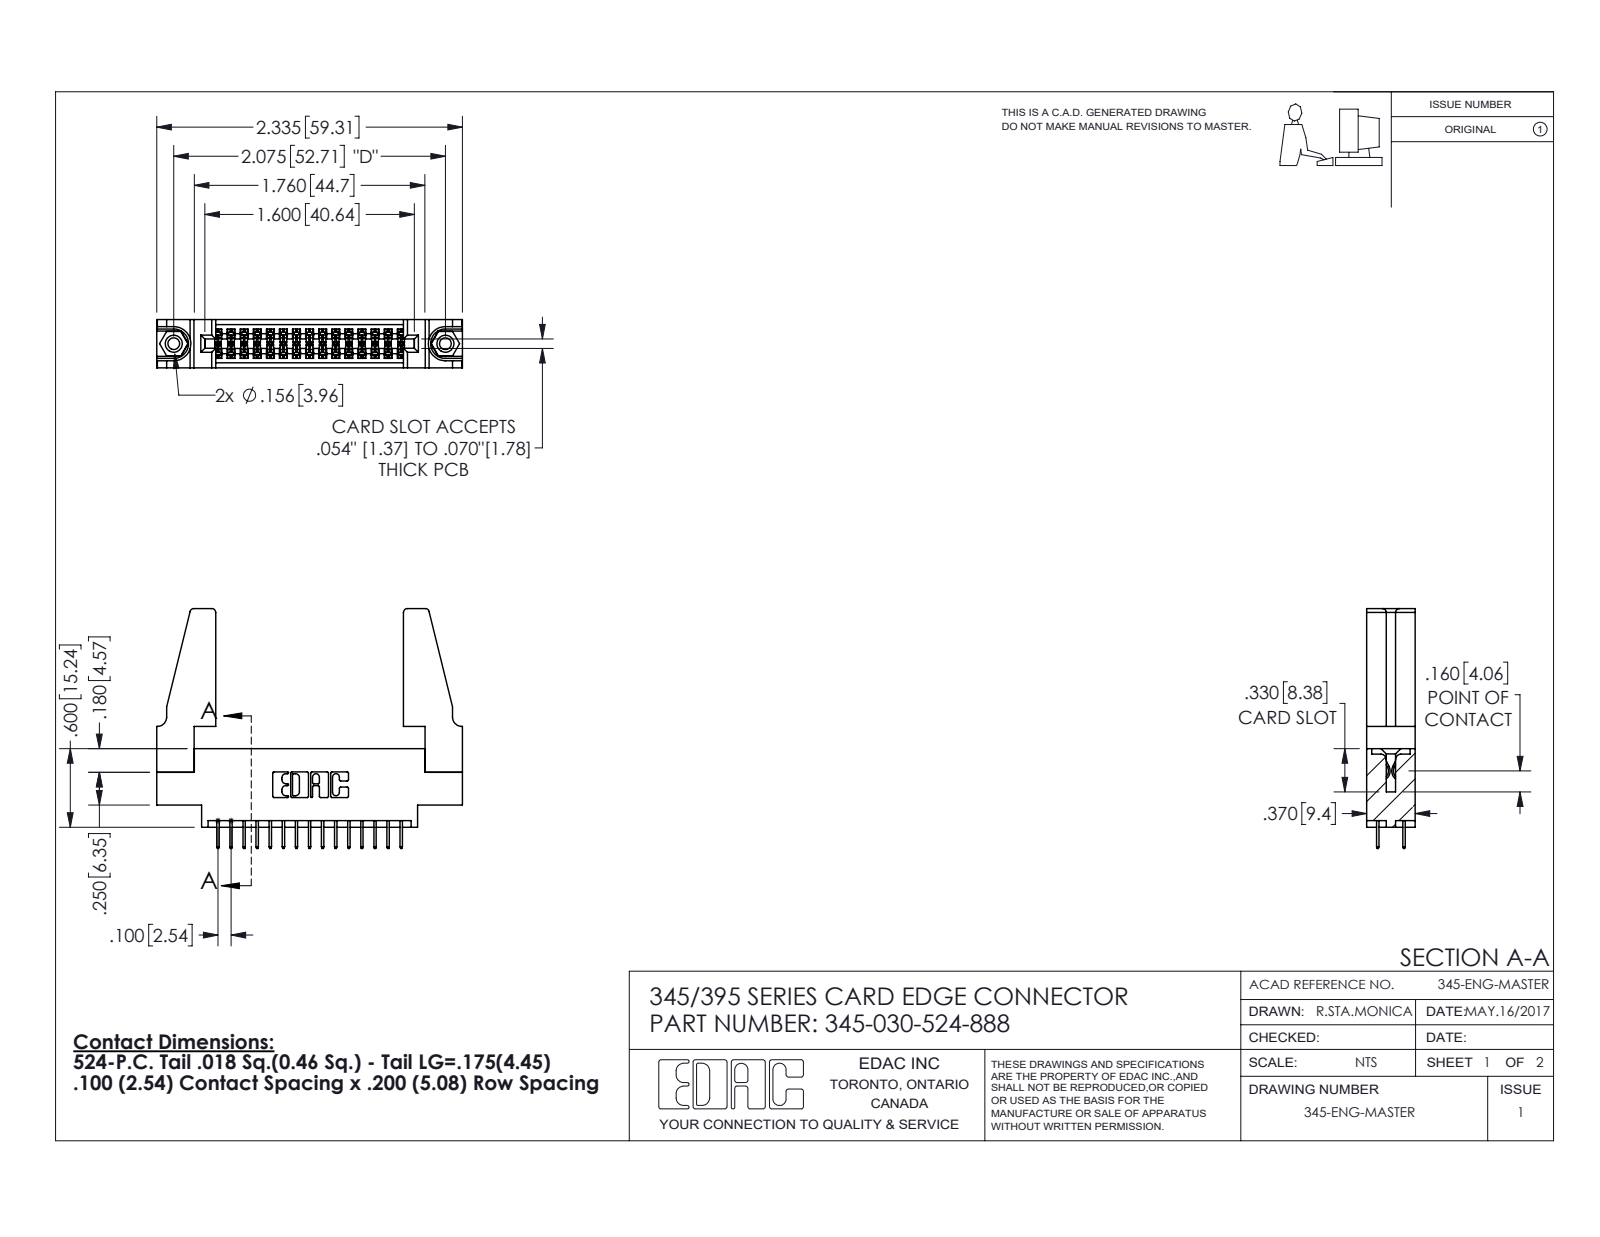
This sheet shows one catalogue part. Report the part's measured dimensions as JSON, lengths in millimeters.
{"part_name": "345-220-078_345-220-088; 345-250-001_345-250-001-102; 345-292-001_345-293-124; 345 Part_0.170 Offset - 0.156 Dia-TH (+1 more)", "step_written_by": "SolidWorks 2016 (CONFIG_CONTROL_DESIGN)", "units": "millimeters", "bodies": {"solids": 35, "faces": 1874, "planar": 1326, "cylindrical": 532, "other": 16}, "overall_size": [59.3, 46.5, 9.4], "volume_mm3": 8600, "surface_area_mm2": 10540, "round_holes": [[2.3, 2], [3.2, 2], [4, 2], [1.6, 1]], "round_bosses_or_shafts": [[3.9, 2]], "partial_cylinders_radius": [[0.2, 45], [0.3, 22], [0.8, 8], [0.2, 6], [0.8, 6], [0.7, 3], [0.4, 2], [0.5, 2]], "face_to_face_distances": [9.4, 1.8, 7.6, 5.1, 2.5, 6.9, 0.6, 5.7, 4.4, 3.8], "hole_center_spacings": [6.9, 46.8, 52.7]}
